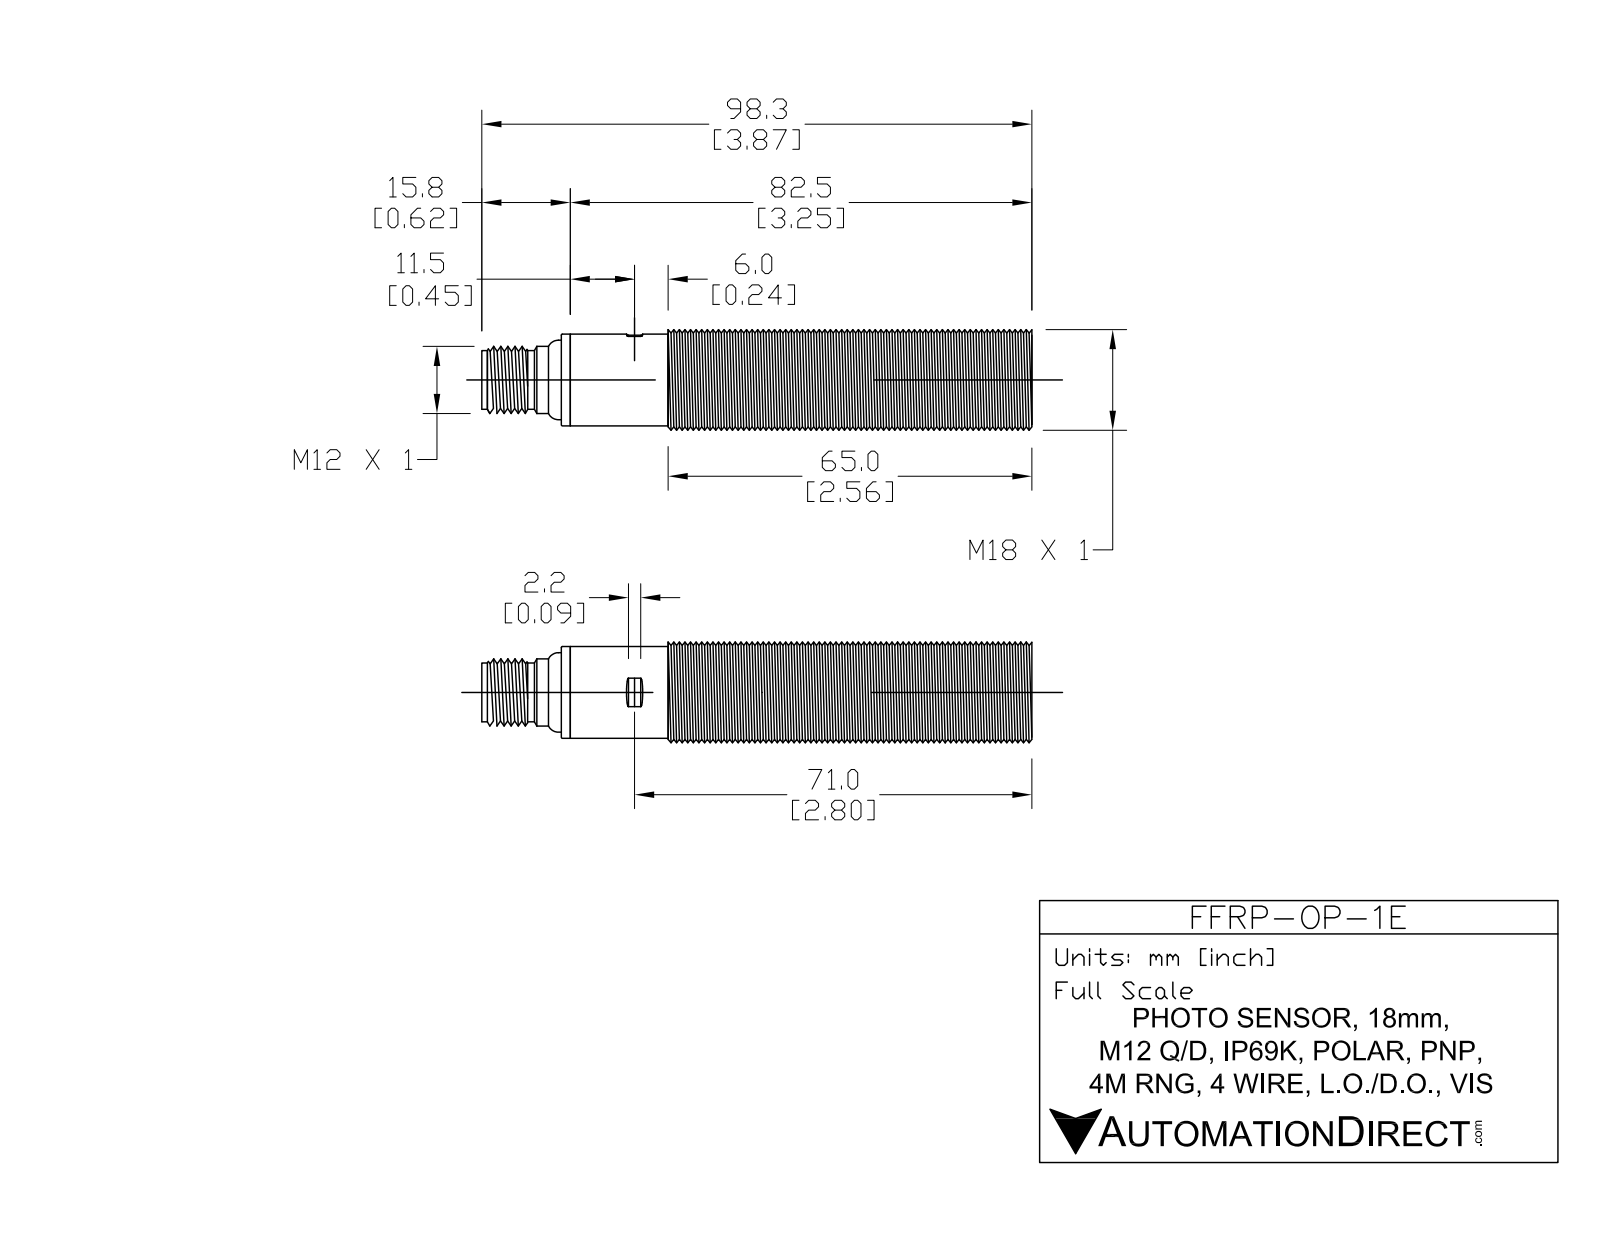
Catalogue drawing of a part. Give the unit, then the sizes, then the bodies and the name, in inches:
Units: inches
Overall size (bounding box): 3.268 × 0.709 × 0.709
Round holes (diameter × count): ⌀0.278 ×1, ⌀0.327 ×1, ⌀0.5 ×1, ⌀0.583 ×1, ⌀0.61 ×1
Round bosses / shafts (diameter × count): ⌀0.039 ×4, ⌀0.709 ×1, ⌀0.646 ×1, ⌀0.612 ×1, ⌀0.604 ×1, ⌀0.559 ×1, ⌀0.492 ×1, ⌀0.472 ×1
Partial cylindrical surfaces — rounded edges, fillets, slot ends (radius × count): R0.024 ×1, R0.63 ×1
Main face-to-face distances: 2.539, 0.118, 2.657, 0.024, 0.094, 2.634, 2.717, 2.693, 2.598, 0.059
Volume: 1.081 in³ · Surface area: 10.47 in²
Bodies: 5 solids, 118 faces (21 planar, 48 cylindrical, 49 other)
Part name (STEP PRODUCT): FFRP-0P-1E
STEP written by: SolidWorks 2017 (AUTOMOTIVE_DESIGN)
